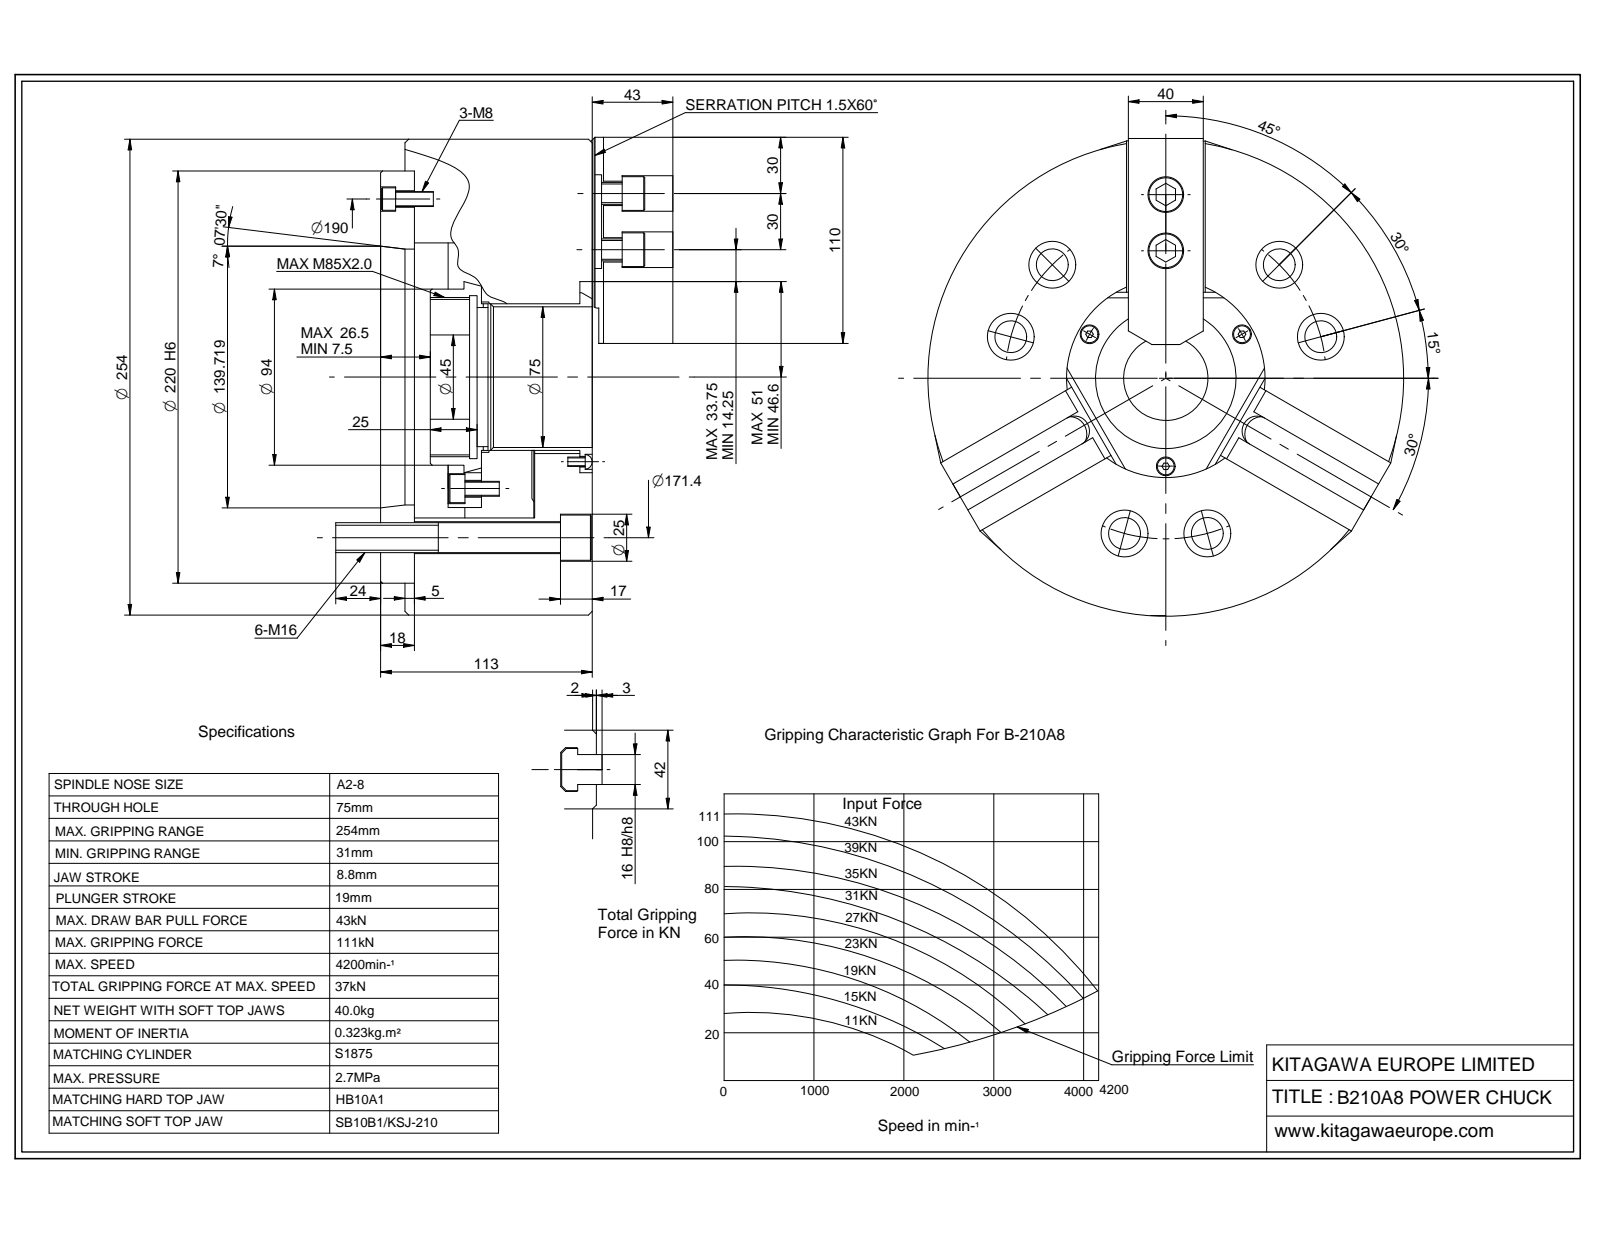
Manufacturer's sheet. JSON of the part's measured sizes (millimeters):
{"part_name": "B210A8-15D", "step_written_by": "ST-DEVELOPER v16.7 (AUTOMOTIVE_DESIGN)", "units": "millimeters", "bodies": {"solids": 1, "faces": 3730, "planar": 3096, "cylindrical": 297, "other": 337}, "overall_size": [254, 254, 180.2], "volume_mm3": 4872000, "surface_area_mm2": 563570, "round_holes": [[17, 18], [3.8, 9], [11, 9], [25, 9], [12, 8], [6, 7], [8.38, 6], [10, 6], [13, 6], [19, 6], [1.5, 3], [1.9, 3]], "round_bosses_or_shafts": [[16, 12], [24, 6], [18, 6], [10.5, 3], [254, 1], [150, 1], [142.7, 1], [89, 1]], "partial_cylinders_radius": [[0.45, 12], [0.6, 12], [1.2, 6], [6.5, 6], [6.75, 6], [9.5, 6], [3.1, 3], [8.3, 3]], "face_to_face_distances": [113, 40, 37.5, 1, 13, 100, 12, 10.5, 18, 156.2], "hole_center_spacings": [128.49, 62, 87.32, 101.32, 105.8, 123.95, 148.48, 27.4]}
